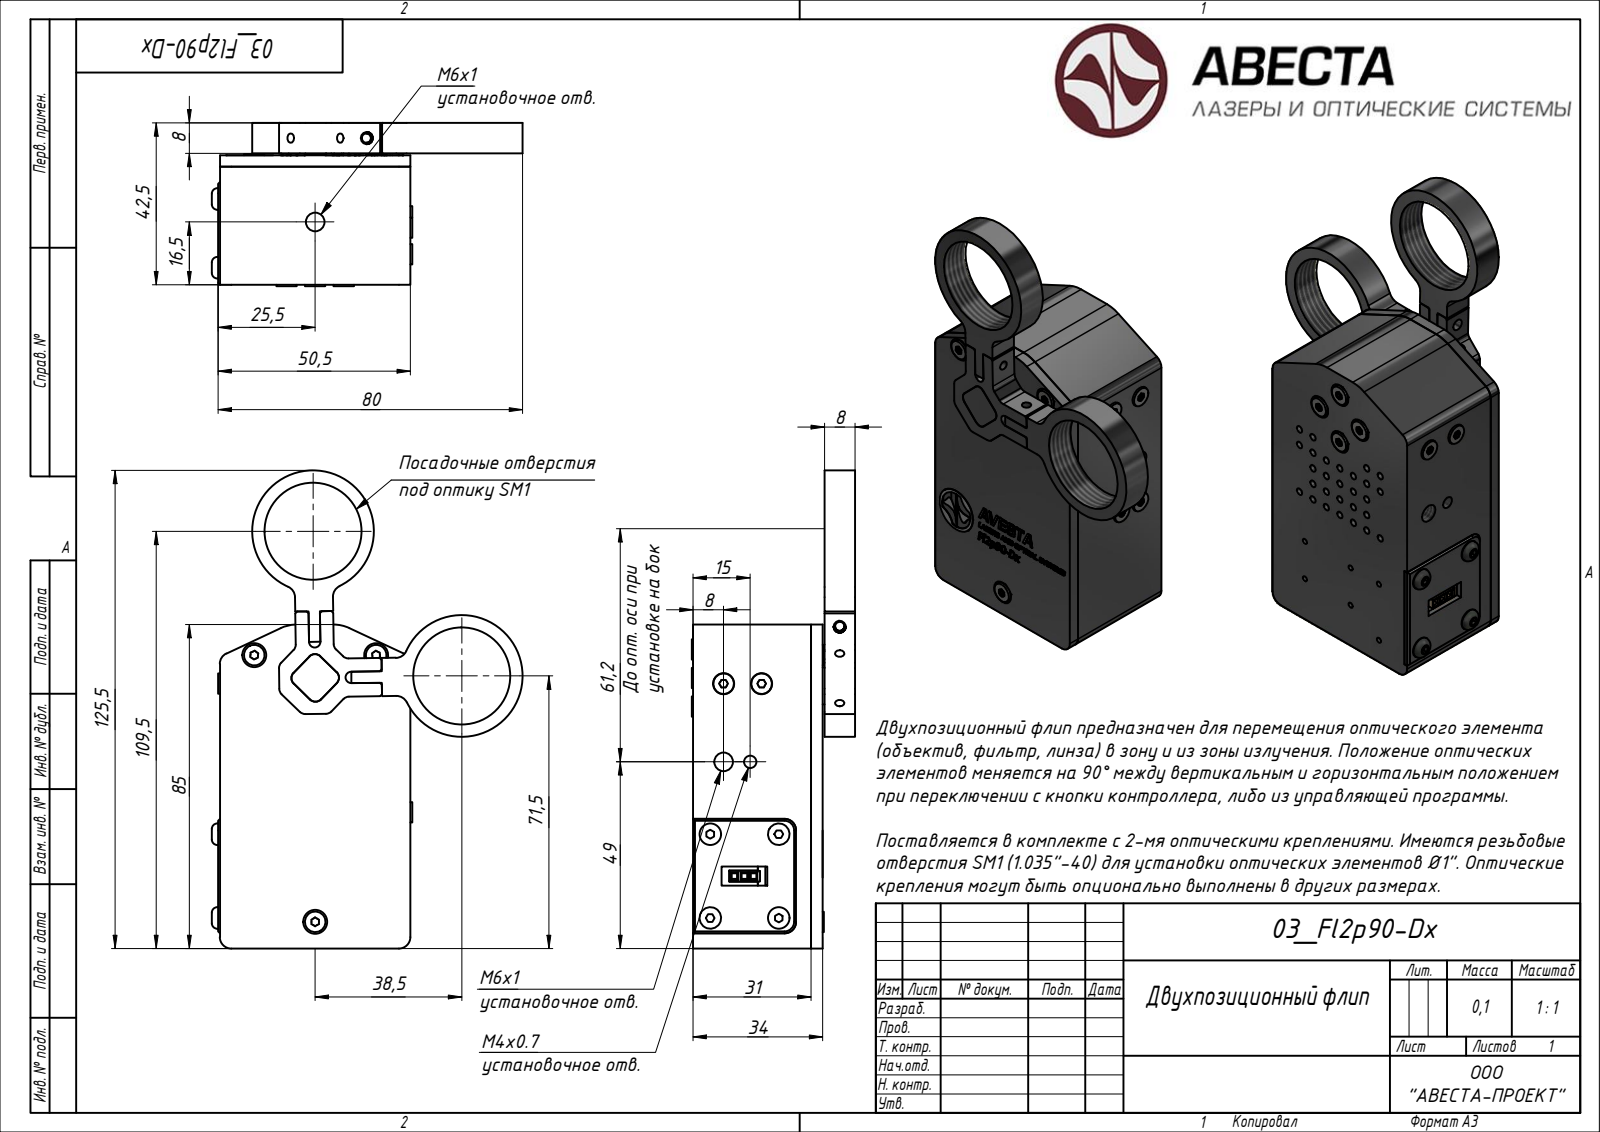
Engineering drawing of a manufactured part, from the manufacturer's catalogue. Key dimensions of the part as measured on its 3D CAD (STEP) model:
STEP written by: Rhino 7.34 (AUTOMOTIVE_DESIGN)
Units: millimetres
Bodies: 6 solids, 833 faces (364 planar, 357 cylindrical, 112 other)
Overall size (bounding box): 125.5 × 81.65 × 42.84
Volume: 62 518 mm³ · Surface area: 40 955 mm²
Round holes (diameter × count): ⌀2 ×28, ⌀3.4 ×7, ⌀1.57 ×5, ⌀2.9 ×3, ⌀2.46 ×2, ⌀3.2 ×2, ⌀25.48 ×2, ⌀1.57 ×1, ⌀2.46 ×1, ⌀3.24 ×1, ⌀4.92 ×1, ⌀4.92 ×1
Round bosses / shafts (diameter × count): ⌀3 ×15, ⌀5.35 ×11, ⌀5.7 ×4, ⌀32 ×2, ⌀20 ×1
Partial cylindrical surfaces — rounded edges, fillets, slot ends (radius × count): R3 ×26, R2 ×19, R1 ×12, R1.01 ×11, R0.5 ×7, R5 ×4, R10 ×4, R2.5 ×3
Main face-to-face distances: 3, 34, 31, 47, 29, 32, 2, 1, 0.5, 28
Hole centre spacings: 11.18, 5, 7.07, 15.81, 10, 18.03, 15, 14.14
